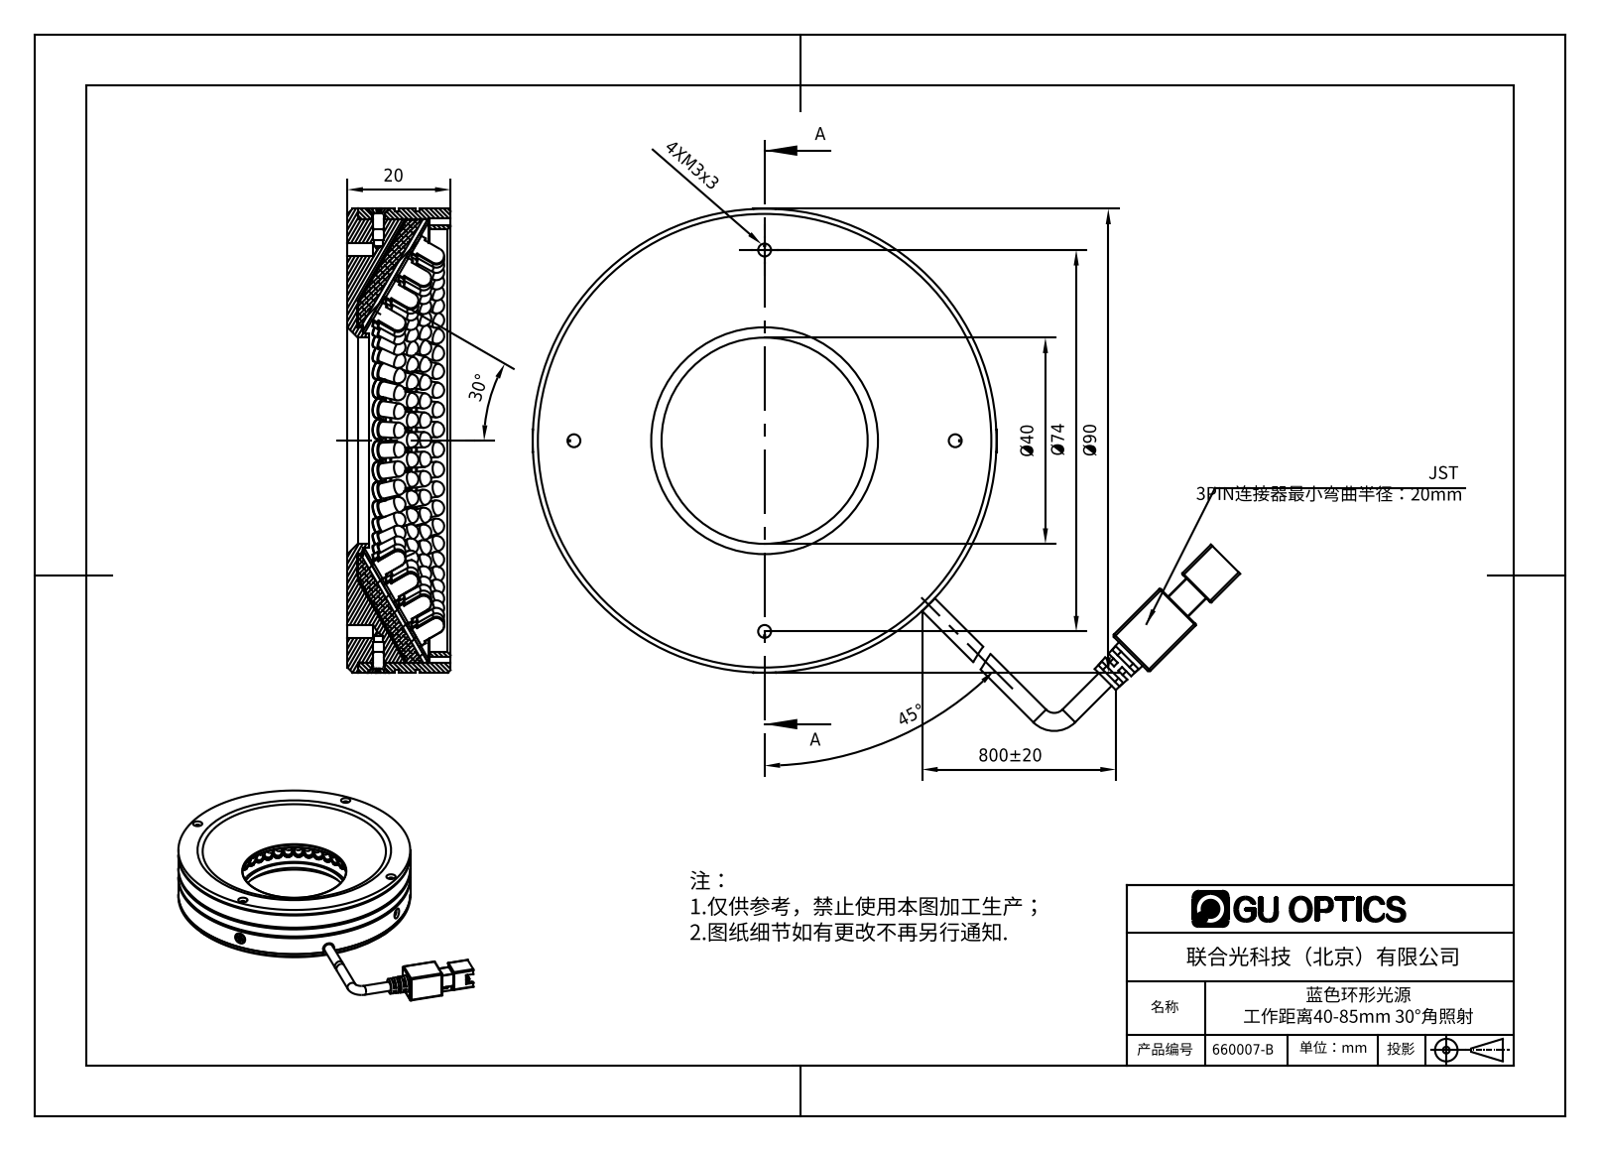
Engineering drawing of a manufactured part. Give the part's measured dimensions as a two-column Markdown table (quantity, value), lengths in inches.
| quantity | value |
| --- | --- |
| part name | 660007-B |
| STEP written by | SolidWorks 2016 (AUTOMOTIVE_DESIGN) |
| units | inches |
| bodies | 201 solids, 4314 faces (2669 planar, 1337 cylindrical, 308 other) |
| overall size | 5.405 × 3.989 × 0.951 |
| volume | 4.808 in³ |
| surface area | 122 in² |
| round holes (diameter × count) | 0.049 × 4, 0.071 × 4, 0.098 × 4, 0.063 × 2, 0.079 × 2, 0.094 × 2, 1.575 × 1, 1.732 × 1, 3.228 × 1 |
| round bosses / shafts (diameter × count) | 0.15 × 248, 0.118 × 192, 0.138 × 2, 3.543 × 1, 3.504 × 1, 3.386 × 1, 1.756 × 1, 1.642 × 1 |
| partial cylindrical surfaces (radius × count) | 0.008 × 37, 0.004 × 15, 0.016 × 12, 0.012 × 1, 0.027 × 1, 0.055 × 1, 0.065 × 1, 0.354 × 1 |
| main face-to-face distances | 0.787, 0.079, 0.866, 0.709, 0.039, 0.02, 0.157, 0.236, 0.118, 0.551 |
| hole center spacings | 0.217, 1.673, 2.219, 3.13, 3.346, 2.366, 1.457, 2.06 |
